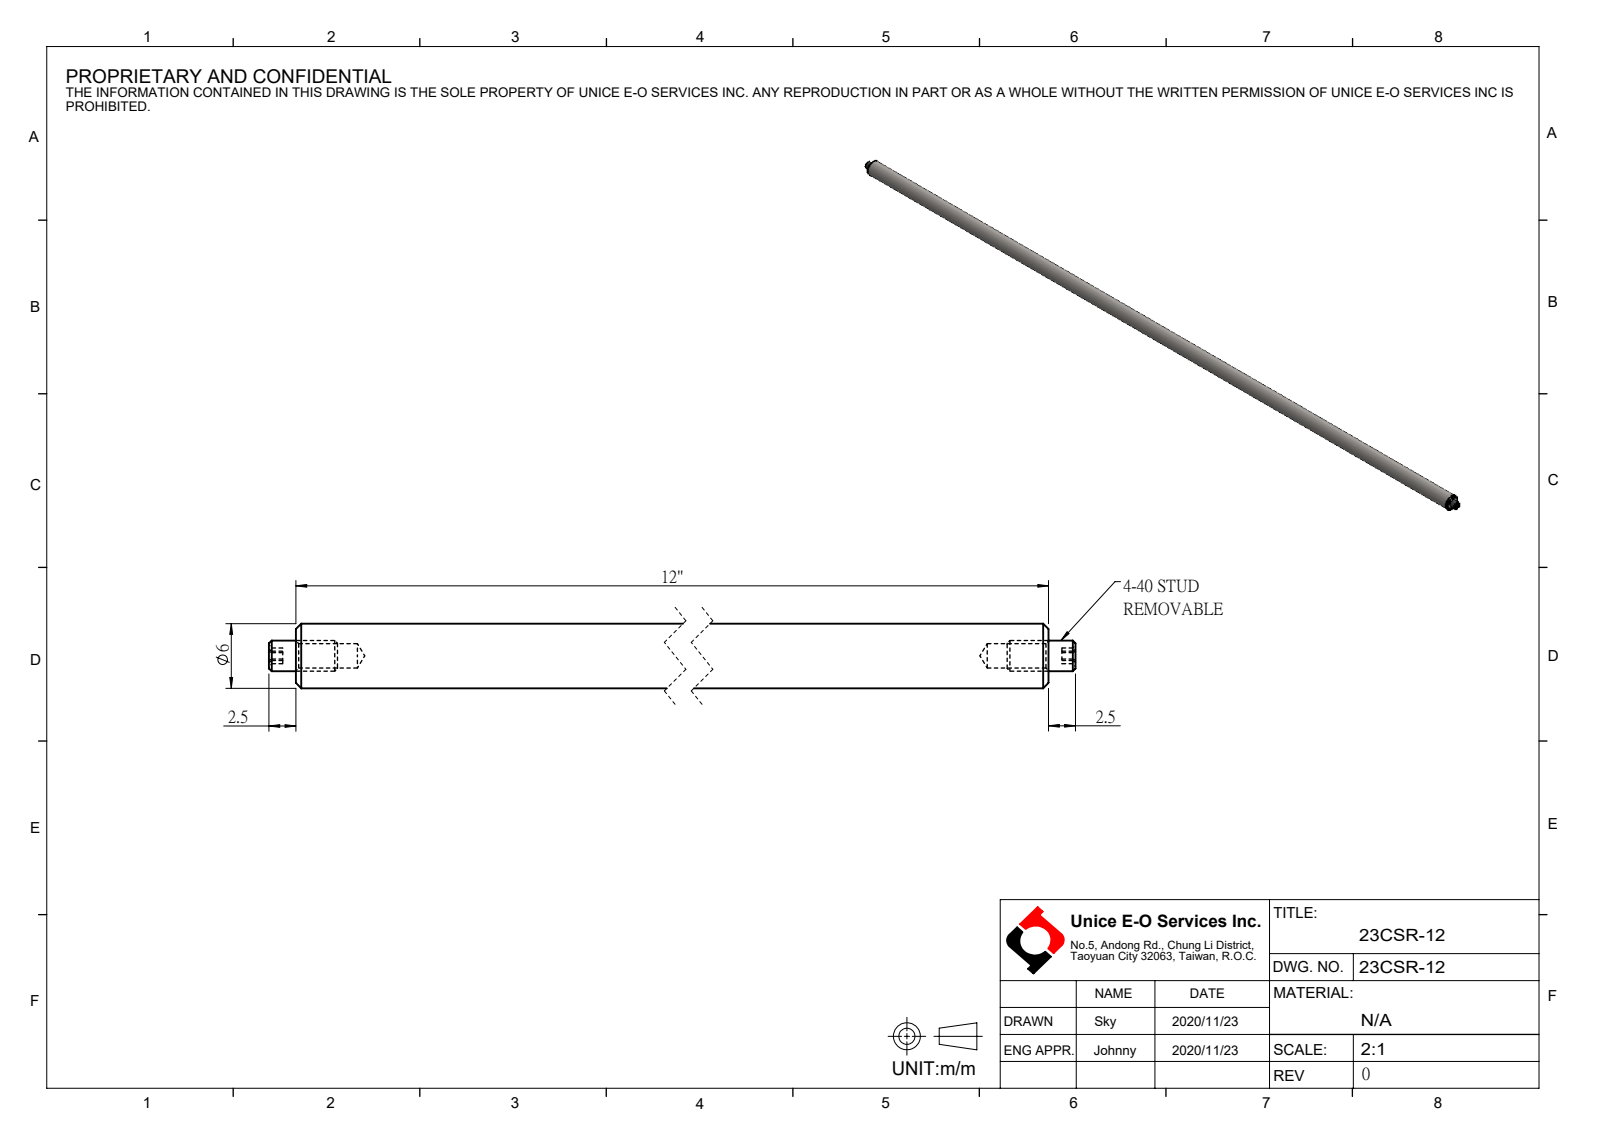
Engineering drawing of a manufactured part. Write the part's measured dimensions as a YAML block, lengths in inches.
part_name: "23CSR-12"
step_written_by: "SolidWorks 2016 (AUTOMOTIVE_DESIGN)"
units: inches
bodies: {solids: 0, faces: 38, planar: 24, cylindrical: 6, other: 8}
overall_size: [12.197, 0.236, 0.236]
round_bosses_or_shafts:
  - {diameter: 0.236, count: 1}
  - {diameter: 0.112, count: 1}
face_to_face_distances: [12, 0.05, 0.098, 12.098, 12.197]
